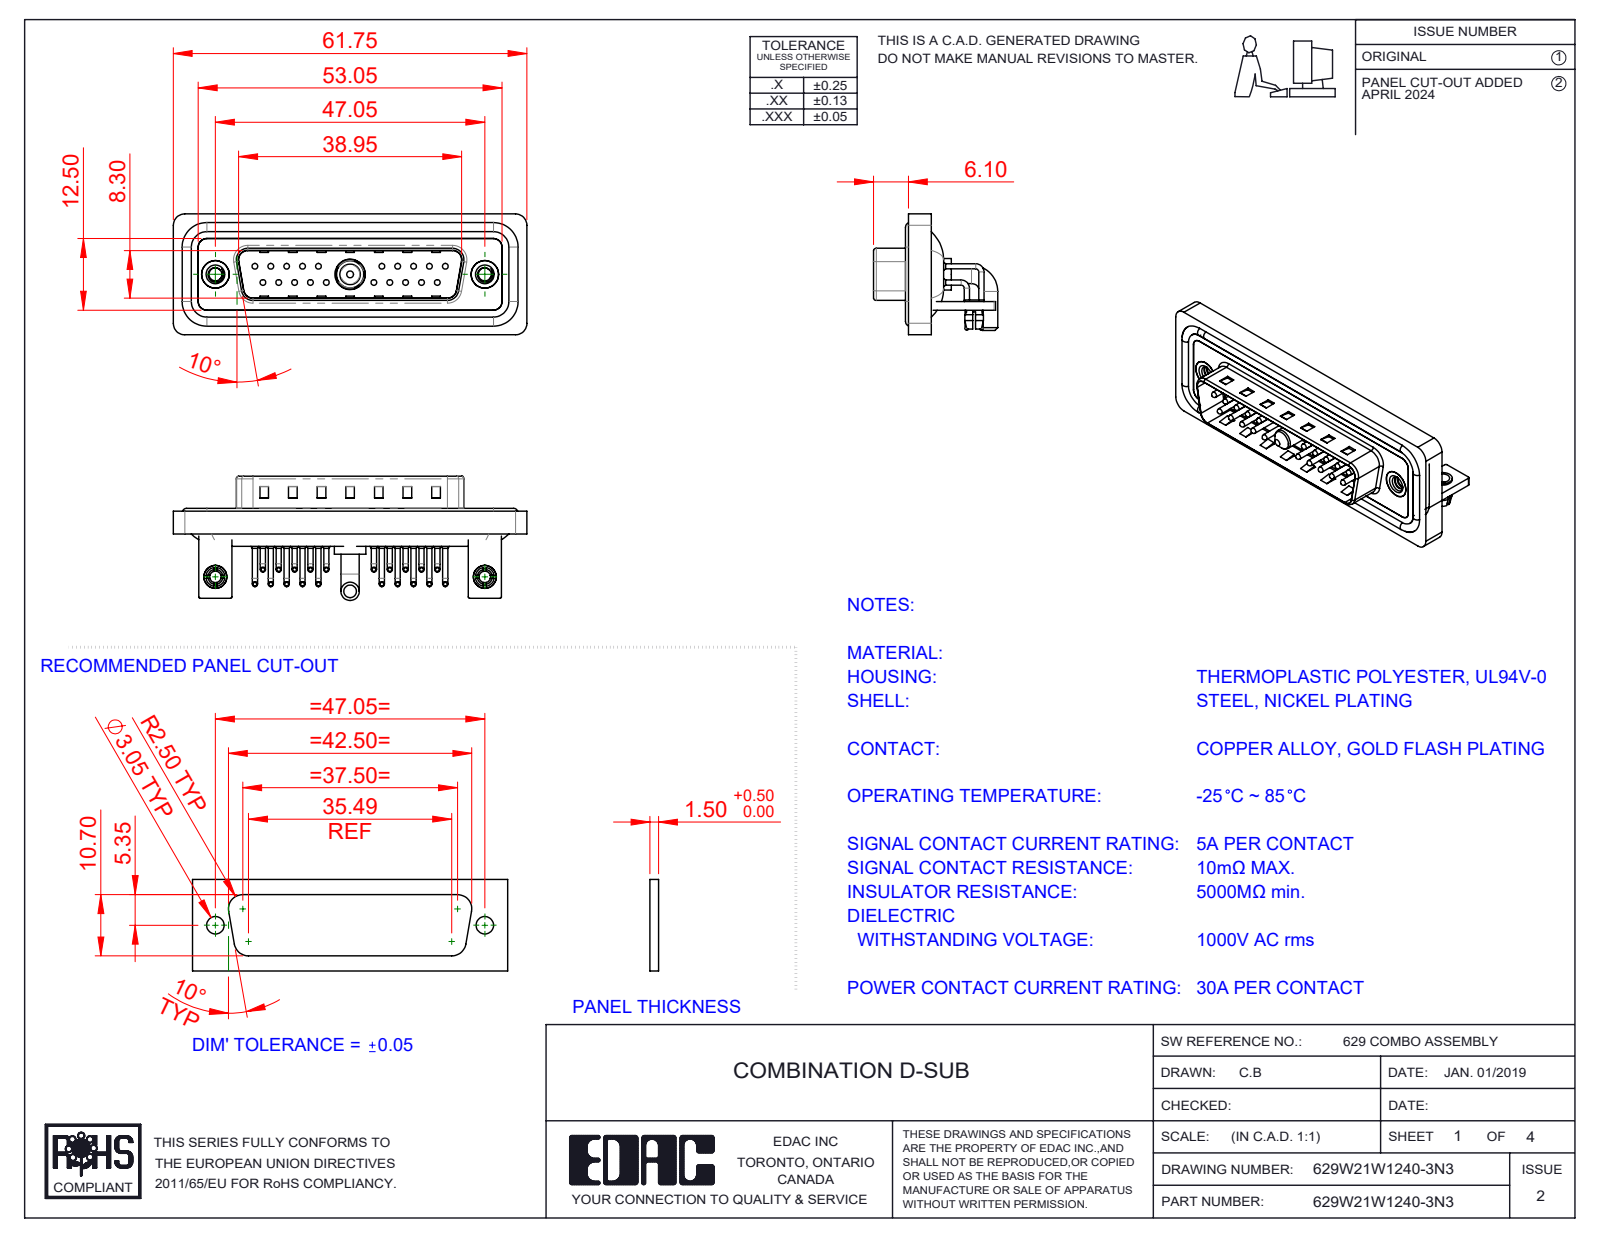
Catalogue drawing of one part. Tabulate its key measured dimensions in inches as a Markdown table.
| quantity | value |
| --- | --- |
| part name | 629Combo Threaded Rivet_3; 629Combo Contact Row 2; 629Combo Housing_21W1; 629W21W1240-3N3 (+7 more) |
| STEP written by | SolidWorks 2023 (CONFIG_CONTROL_DESIGN) |
| units | inches |
| bodies | 33 solids, 2858 faces (1567 planar, 979 cylindrical, 312 other) |
| overall size | 2.431 × 0.854 × 0.831 |
| volume | 0.474 in³ |
| surface area | 20.98 in² |
| round holes (diameter × count) | 0.079 × 22, 0.03 × 20, 0.063 × 20, 0.089 × 2, 0.098 × 2, 0.126 × 2, 0.157 × 2, 0.189 × 2, 0.197 × 2, 0.191 × 1, 0.209 × 1 |
| round bosses / shafts (diameter × count) | 0.035 × 40, 0.059 × 20, 0.039 × 20, 0.026 × 20, 0.063 × 4, 0.193 × 2, 0.157 × 2, 0.134 × 2 |
| partial cylindrical surfaces (radius × count) | 0.04 × 20, 0.079 × 19, 0.059 × 18, 0.01 × 16, 0.02 × 9, 0.063 × 8, 0.024 × 4, 0.026 × 4 |
| main face-to-face distances | 0.016, 0.031, 0.083, 0.114, 0.059, 0.043, 0.161, 0.063, 0.177, 0.146 |
| hole center spacings | 0.124, 0.109, 0.218, 0.327, 0.198, 0.763, 0.826, 0.872 |
